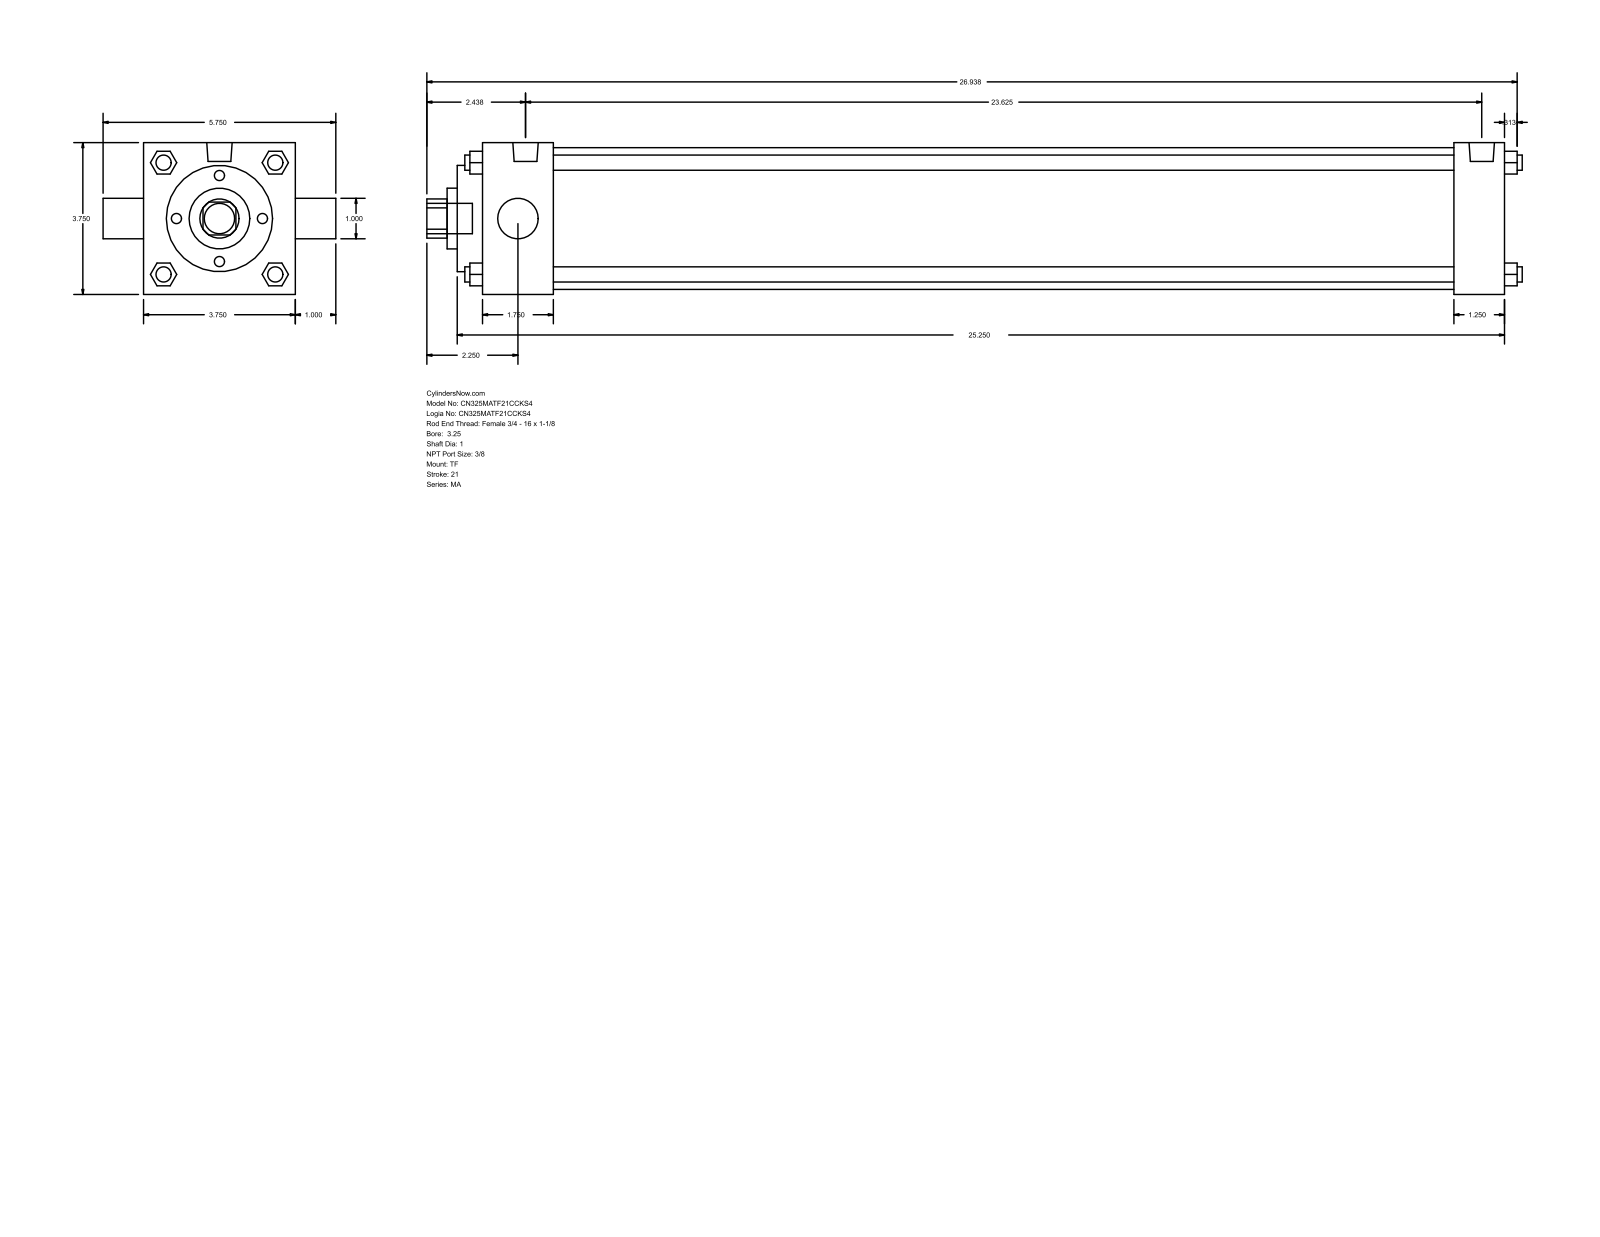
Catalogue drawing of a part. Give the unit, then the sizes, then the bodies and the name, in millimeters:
Units: millimetres
Overall size (bounding box): 687.39 × 146.05 × 95.25
Round holes (diameter × count): ⌀25.4 ×2, ⌀38.1 ×1, ⌀66.67 ×1, ⌀88.9 ×1
Round bosses / shafts (diameter × count): ⌀9.53 ×4, ⌀11.11 ×3, ⌀15.93 ×2, ⌀19.05 ×1
Partial cylindrical surfaces — rounded edges, fillets, slot ends (radius × count): R12.29 ×1
Main face-to-face distances: 95.24, 641.35, 657.22, 15.87, 44.46, 609.6, 565.14, 596.89, 31.75, 60.33
Bodies: 0 solids, 122 faces (93 planar, 29 cylindrical, 0 other)
Part name (STEP PRODUCT): MA_TF__0325_1
STEP written by: GSSL Pune (CONFIG_CONTROL_DESIGN)
